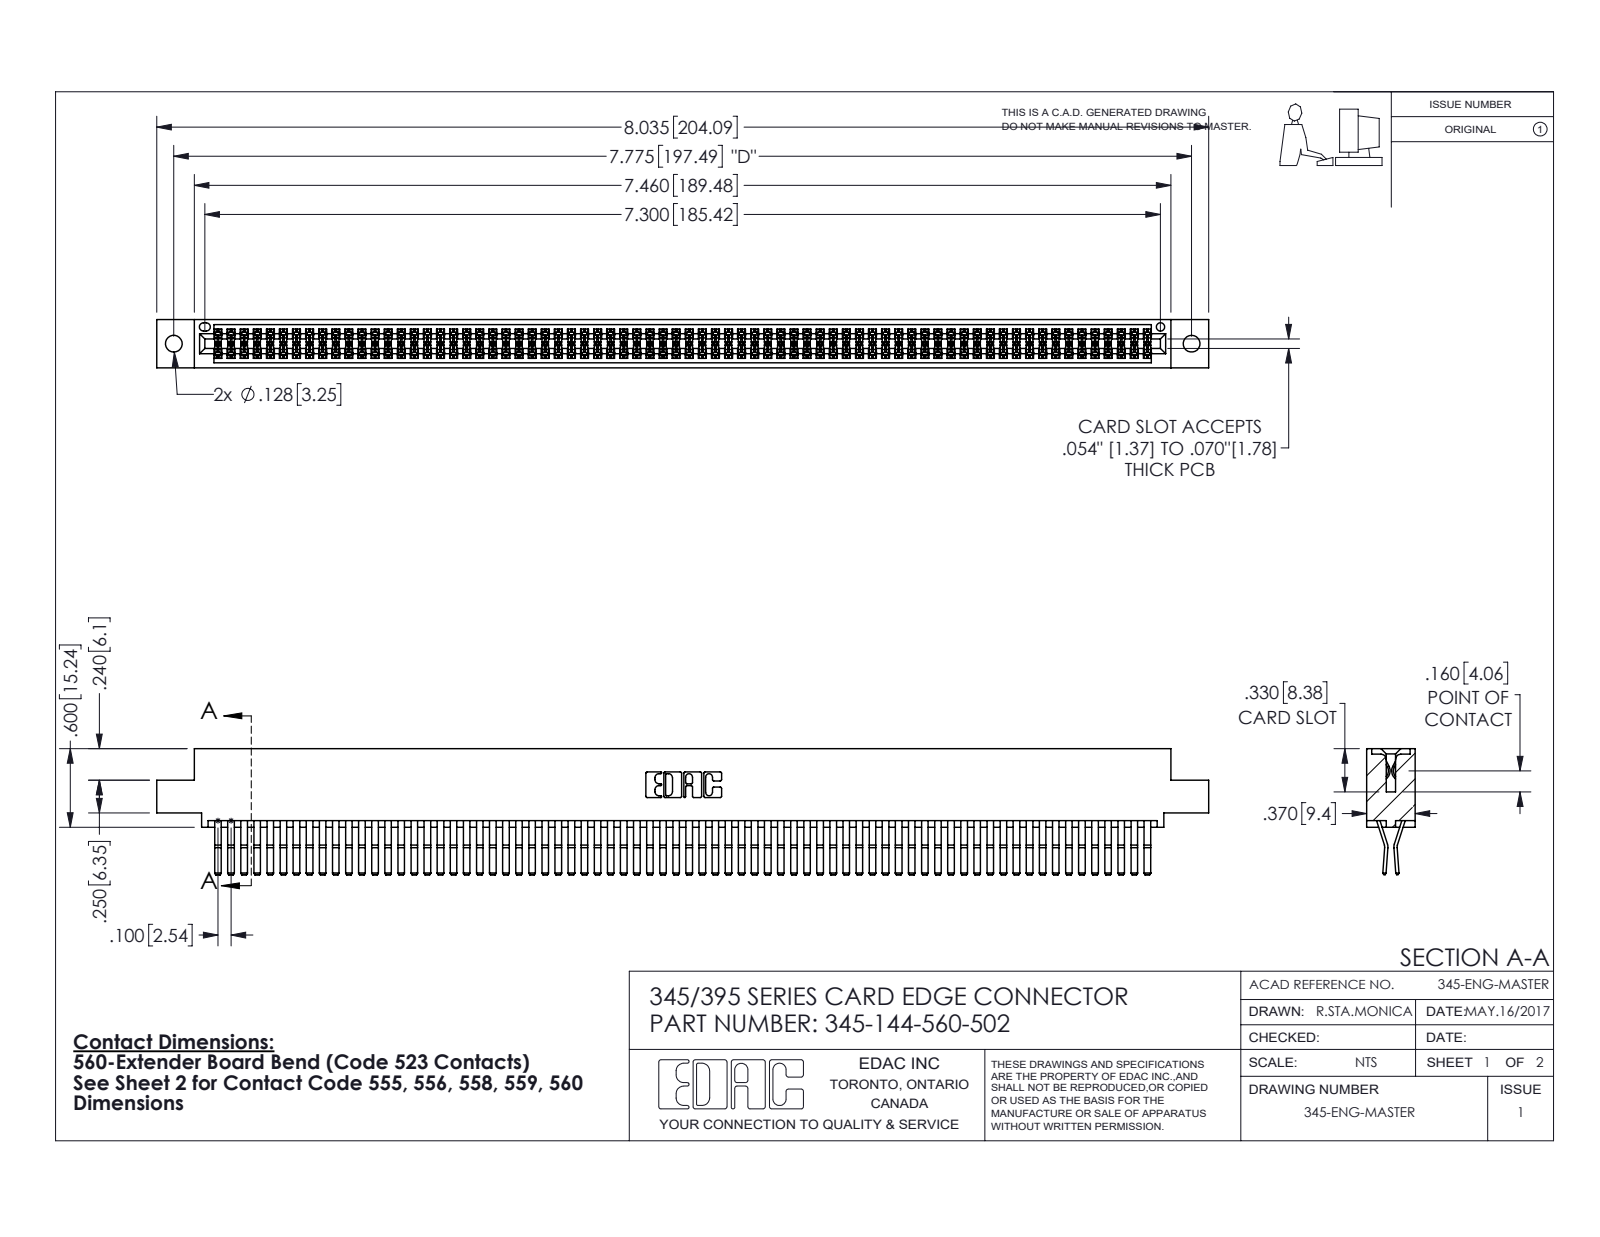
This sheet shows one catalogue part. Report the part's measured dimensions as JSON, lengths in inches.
{"part_name": "345-144-560-502; 345 Part_0.110 Offset - 0.128 Dia; 345-292-001_560 Tail", "step_written_by": "SolidWorks 2016 (CONFIG_CONTROL_DESIGN)", "units": "inches", "bodies": {"solids": 145, "faces": 7618, "planar": 4836, "cylindrical": 2782, "other": 0}, "overall_size": [8.035, 0.962, 0.37], "volume_in3": 1.278, "surface_area_in2": 52.36, "round_holes": [[0.128, 2], [0.064, 1]], "partial_cylinders_radius": [[0.006, 217], [0.01, 22], [0.007, 6], [0.031, 6], [0.026, 3], [0.01, 2], [0.014, 2], [0.019, 2]], "face_to_face_distances": [0.025, 0.298, 0.072, 0.37, 0.2, 0.098, 0.272, 0.225, 0.175, 0.149], "hole_center_spacings": [0.27, 7.539, 7.775]}
